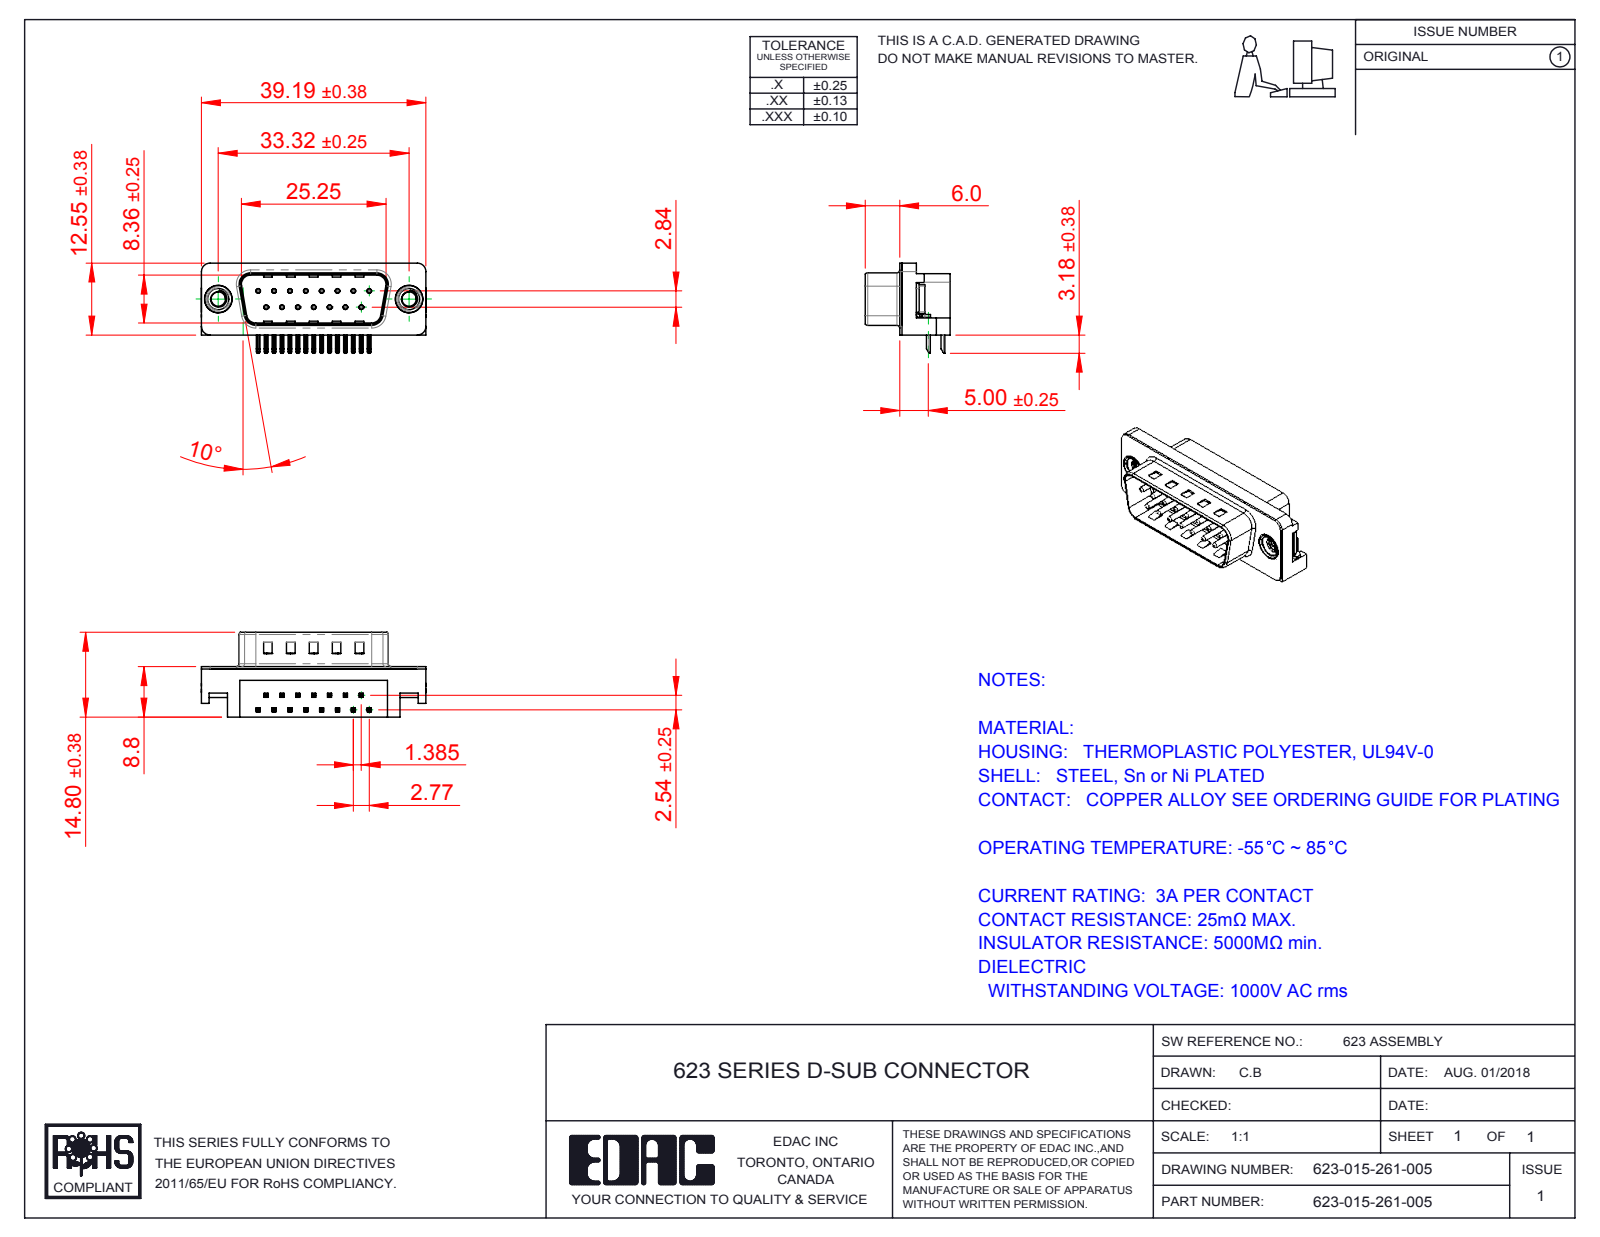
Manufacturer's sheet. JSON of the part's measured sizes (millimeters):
{"part_name": "623 Shell_15 Socket; 623-015-261-005; 623 Contact Top; 623 M3 Threaded Rivet (+3 more)", "step_written_by": "SolidWorks 2016 (CONFIG_CONTROL_DESIGN)", "units": "millimeters", "bodies": {"solids": 21, "faces": 1467, "planar": 893, "cylindrical": 439, "other": 135}, "overall_size": [39.22, 15.73, 14.8], "volume_mm3": 3313, "surface_area_mm2": 4888, "round_holes": [[0.35, 15], [0.8, 15], [2.5, 2], [4, 2], [4.8, 2], [5, 2]], "round_bosses_or_shafts": [[0.75, 15], [4.9, 2], [4.75, 2], [3.9, 2]], "partial_cylinders_radius": [[0.25, 68], [0.12, 30], [1, 16], [0.5, 9], [1.5, 6], [0.9, 4], [1.6, 4], [2, 4]], "face_to_face_distances": [0.4, 8.4, 2.1, 1.7, 10.46, 8.8, 10.86, 8.76, 5.9, 2.9], "hole_center_spacings": [3.16, 2.77, 5.54, 8.31, 11.08, 5.03, 5.04, 7.48]}
